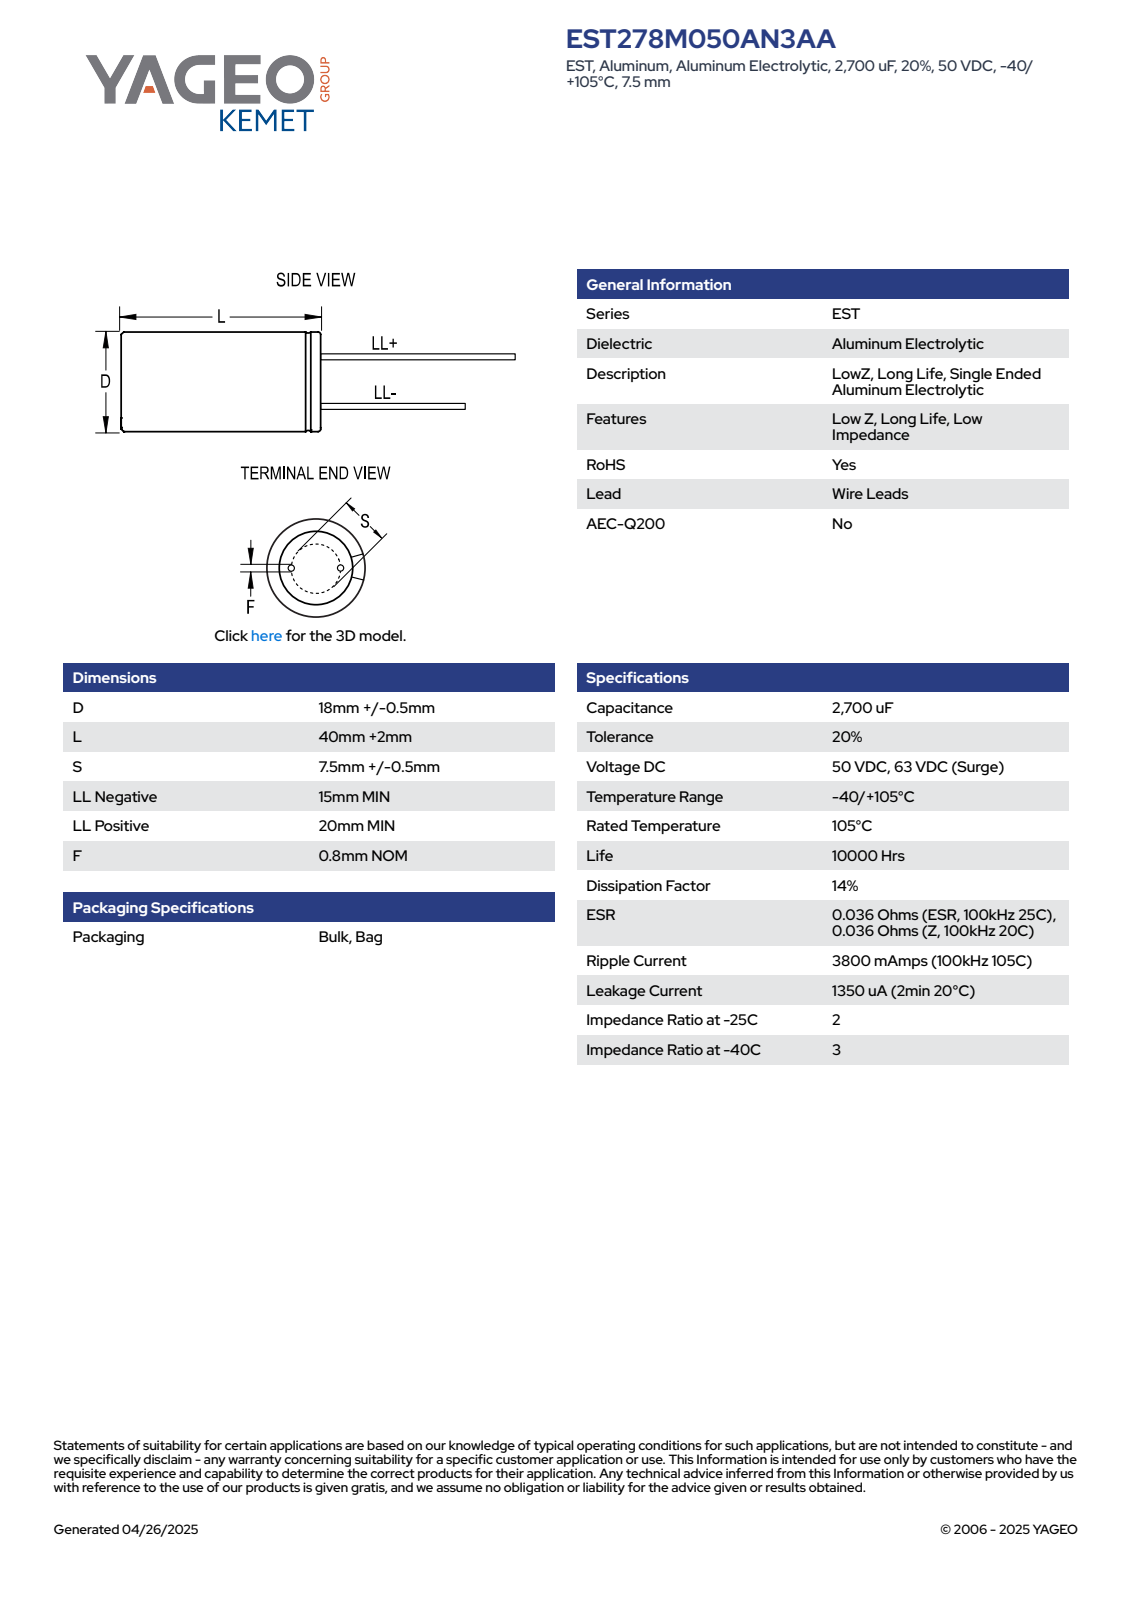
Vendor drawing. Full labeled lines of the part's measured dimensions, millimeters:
Part name (STEP PRODUCT): CAR_KLP_18X40_D18.5L42S7.5F0.8
STEP written by: SolidWorks 2014 (AUTOMOTIVE_DESIGN)
Units: millimetres
Bodies: 4 solids, 75 faces (61 planar, 8 cylindrical, 6 other)
Overall size (bounding box): 62.01 × 18.5 × 18.5
Volume: 11 242 mm³ · Surface area: 3 147 mm²
Round bosses / shafts (diameter × count): ⌀0.8 ×2, ⌀18.5 ×1
Main face-to-face distances: 42, 42.01, 57.01, 62.01, 57, 62, 15, 20, 5, 2.48
